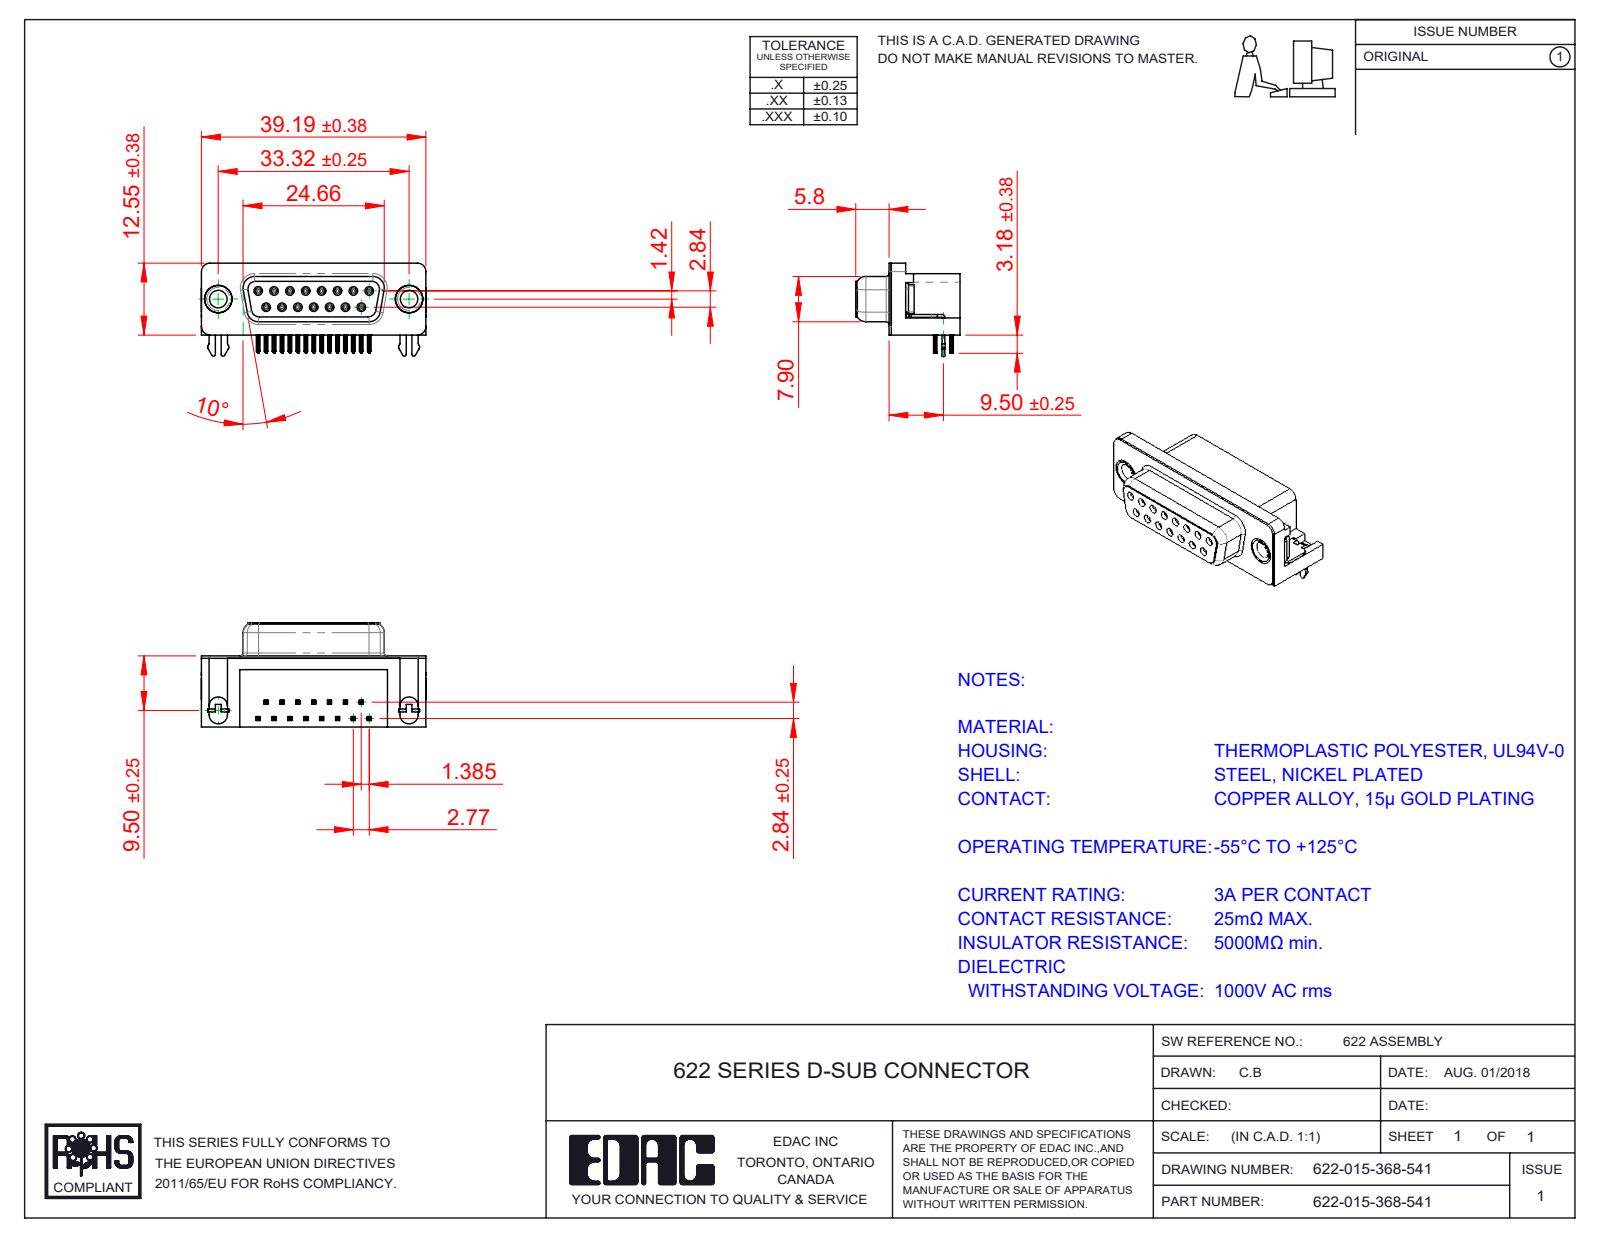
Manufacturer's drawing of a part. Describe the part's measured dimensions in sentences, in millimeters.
The part is named "622-015-368-541; 622 4 Prong Board Lock; 622 Thru Hole Rivet; 622 Socket Bottom (+3 more)". Its 3-D file was written by "SolidWorks 2016 (CONFIG_CONTROL_DESIGN)". It is 21 solids with 2507 faces: 1116 planar, 593 cylindrical and 798 other. Overall it measures 39.22 by 18.2 by 16.25 millimeters. Its volume is 5 185 cubic millimeters and its surface area 6 767 square millimeters. Round holes: 15 of diameter 0.8, 15 of diameter 0.9, 2 of diameter 2, 2 of diameter 3.05, 2 of diameter 4, 2 of diameter 4.8, 2 of diameter 5. Round bosses or shafts: 15 of diameter 1.2, 2 of diameter 4.9, 2 of diameter 4.75, 2 of diameter 3.85, 2 of diameter 3. Partial cylindrical surfaces (rounded edges, fillets, slot ends): 120 of radius 0.1, 60 of radius 0.15, 30 of radius 0.35, 18 of radius 1, 15 of radius 0.34, 12 of radius 0.25, 8 of radius 1.35, 8 of radius 1.5. The main face-to-face distances are 0.4, 12, 6.2, 12.4, 10.35, 2.9, 6.65, 0.85, 0.35, 5.8. The hole center spacings are 3.16, 2.77, 5.54, 8.31, 11.08, 5.03, 5.04, 7.48.
